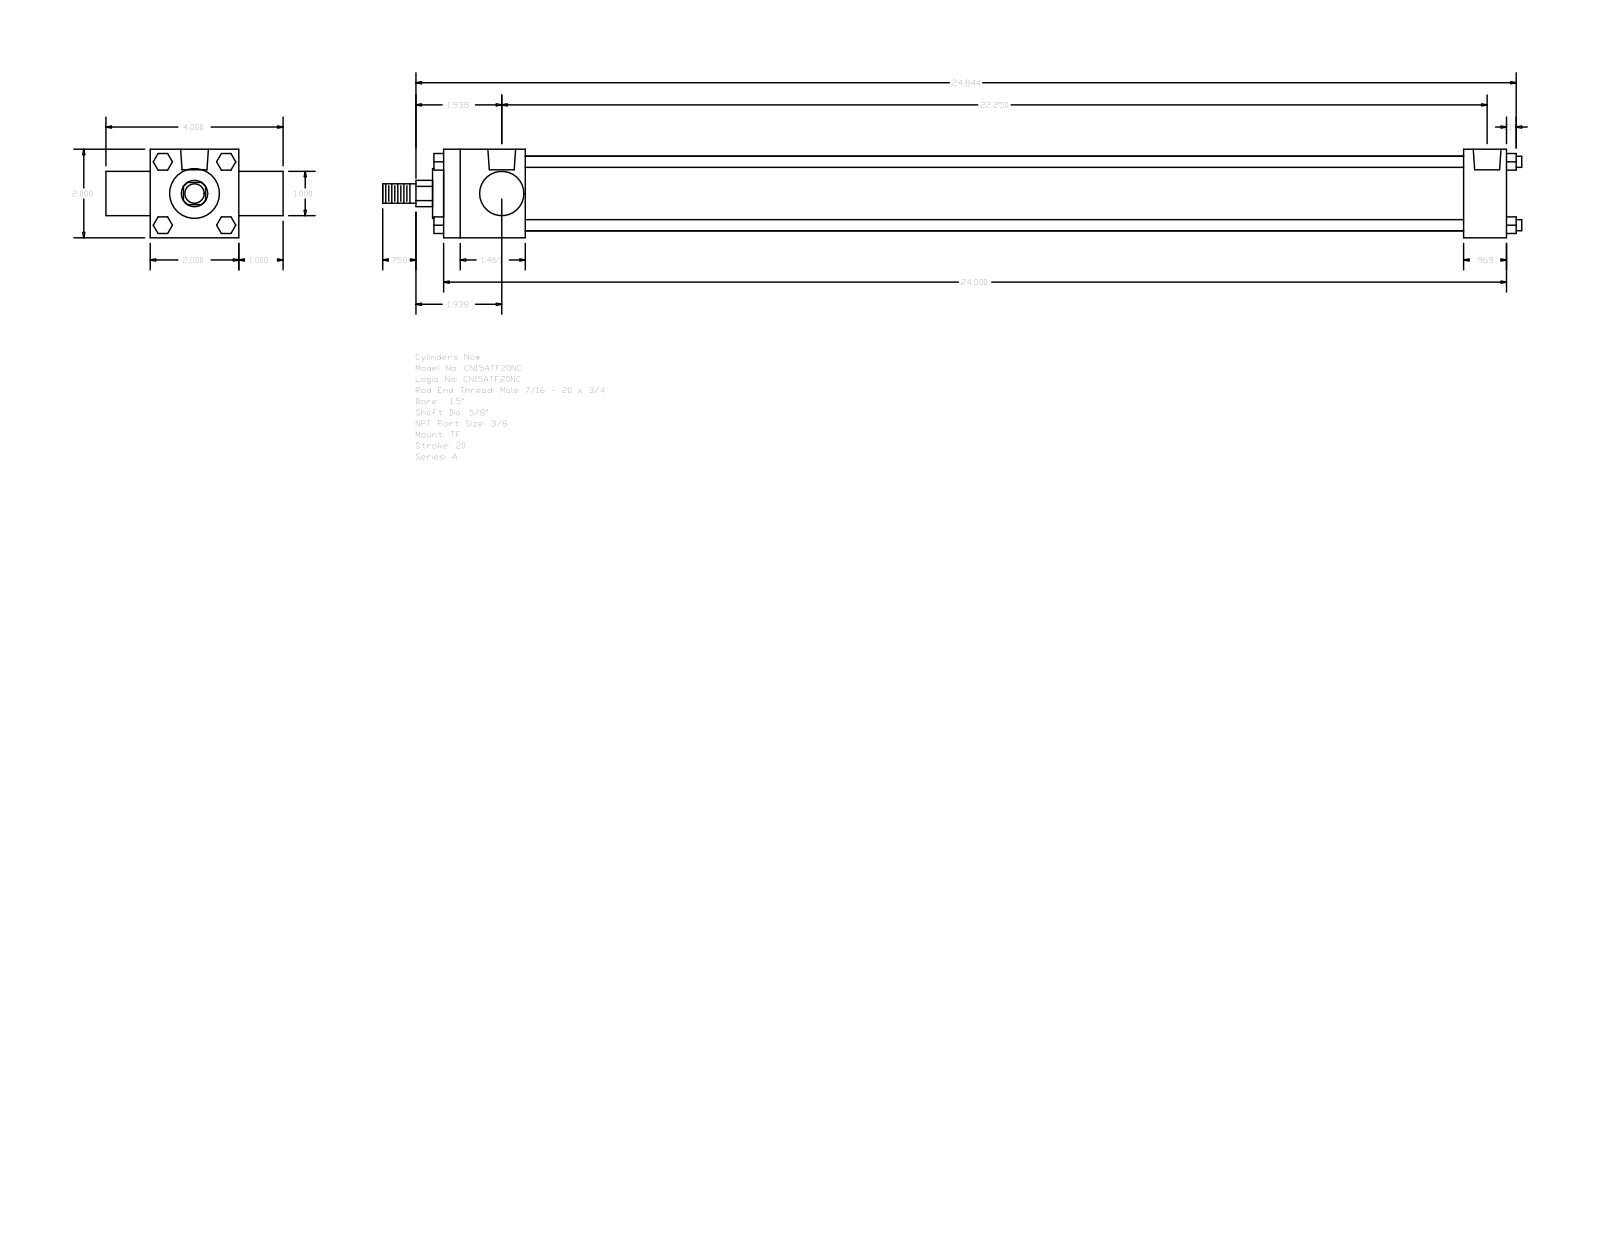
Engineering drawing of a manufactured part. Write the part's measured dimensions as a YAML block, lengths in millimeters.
part_name: "A_TF__0150_0.625"
step_written_by: "GSSL Pune (CONFIG_CONTROL_DESIGN)"
units: millimeters
bodies: {solids: 0, faces: 120, planar: 92, cylindrical: 28, other: 0}
overall_size: [653.26, 101.6, 50.8]
round_holes:
  - {diameter: 5.56, count: 3}
  - {diameter: 15.93, count: 2}
round_bosses_or_shafts:
  - {diameter: 6.35, count: 4}
  - {diameter: 42.93, count: 1}
  - {diameter: 28.57, count: 1}
  - {diameter: 25.4, count: 1}
  - {diameter: 15.88, count: 1}
  - {diameter: 11.11, count: 1}
partial_cylinders:
  - {radius: 7.54, count: 1}
face_to_face_distances: [50.8, 609.6, 25.4, 76.2, 46.83, 584.99, 538.16, 562.77, 24.61, 101.6]
hole_center_spacings: [3.97, 561.18, 557.21, 565.15]
